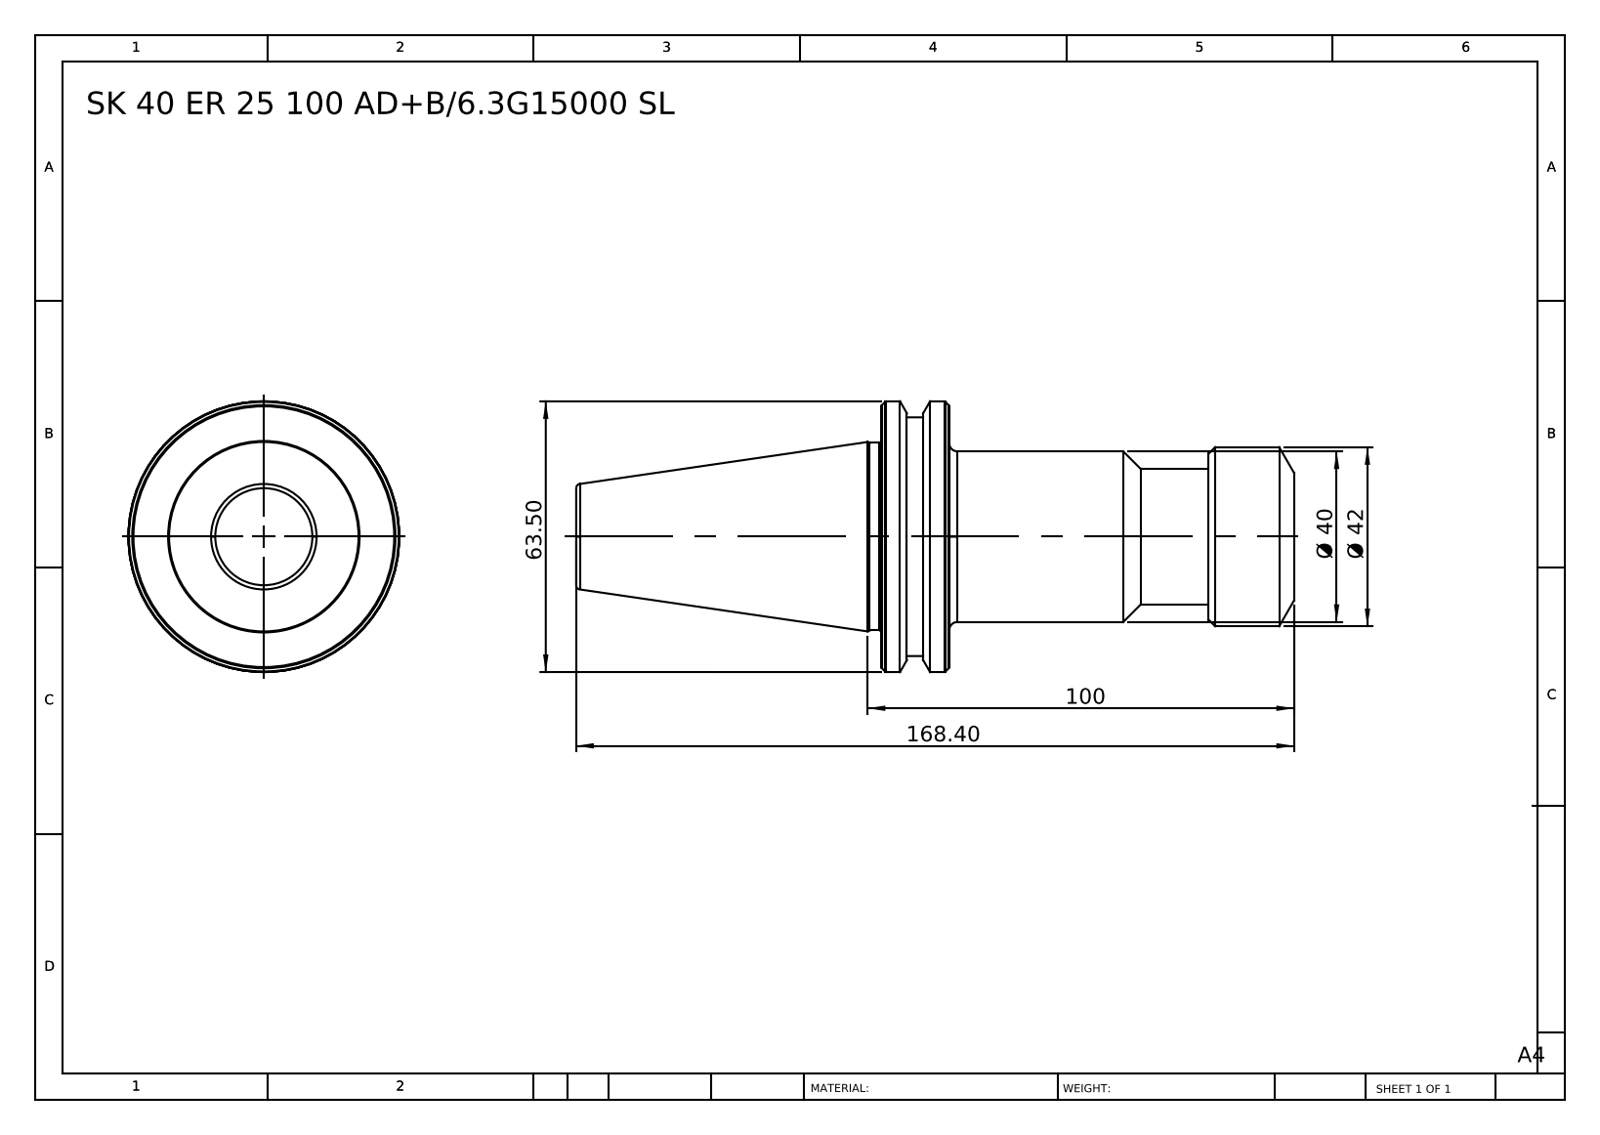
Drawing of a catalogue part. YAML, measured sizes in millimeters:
part_name: "SK 40 ER 25 100 AD-6.3G15000 SL"
step_written_by: "SolidWorks 2014 (CONFIG_CONTROL_DESIGN)"
units: millimeters
bodies: {solids: 1, faces: 57, planar: 3, cylindrical: 8, other: 46}
overall_size: [168.4, 63.51, 63.51]
volume: 211792
surface_area: 27088
round_bosses_or_shafts:
  - {diameter: 44, count: 1}
  - {diameter: 42, count: 1}
  - {diameter: 40, count: 1}
  - {diameter: 31.9, count: 1}
face_to_face_distances: [168.4, 20, 148.4]
